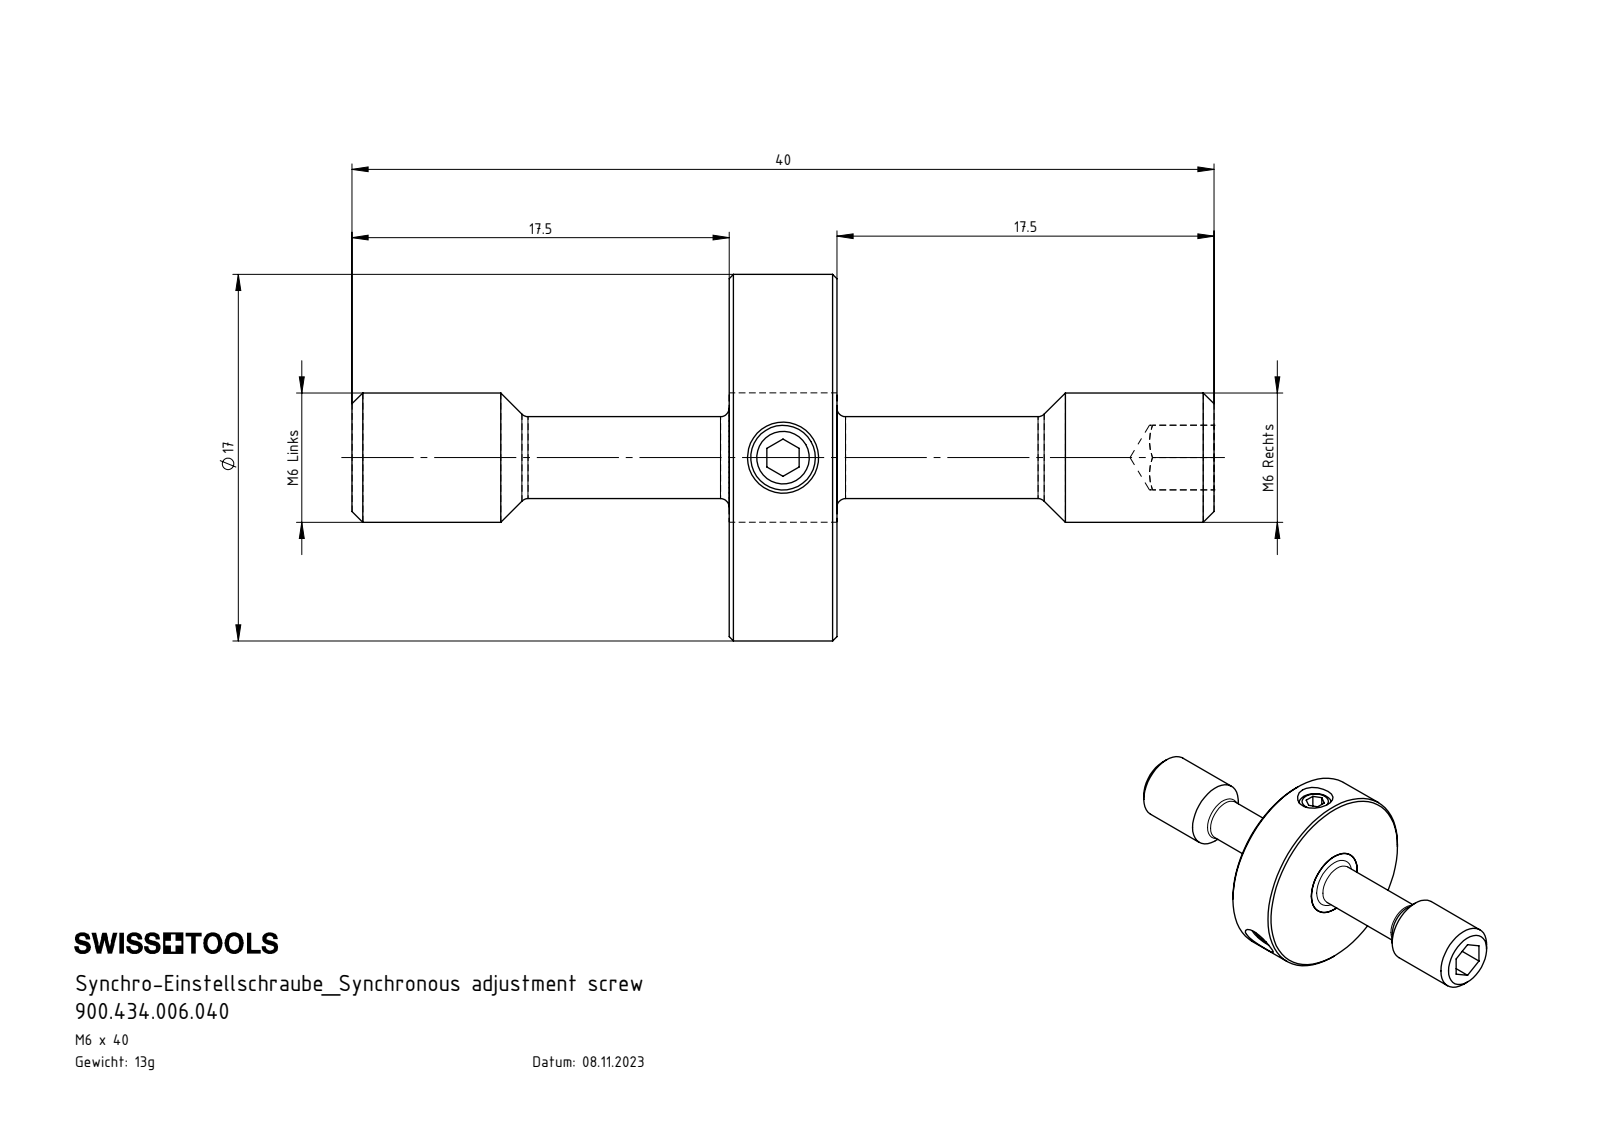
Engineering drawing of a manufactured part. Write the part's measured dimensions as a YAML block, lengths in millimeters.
part_name: "900.434.006.040; Z42-ER3.001.040_A; Z42-ER3.002.005_A; ISO 4026 - M3 x 5"
step_written_by: "SolidWorks 2022 (AUTOMOTIVE_DESIGN)"
units: millimeters
bodies: {solids: 5, faces: 99, planar: 39, cylindrical: 26, other: 34}
overall_size: [40, 17, 17]
volume: 1699
surface_area: 1807
round_holes:
  - {diameter: 3.3, count: 3}
round_bosses_or_shafts:
  - {diameter: 3, count: 3}
  - {diameter: 17, count: 1}
  - {diameter: 6, count: 1}
  - {diameter: 3.8, count: 1}
face_to_face_distances: [5, 17.5, 22.5, 3, 1.5, 40, 19.25, 20.75, 1.75, 3.25]
